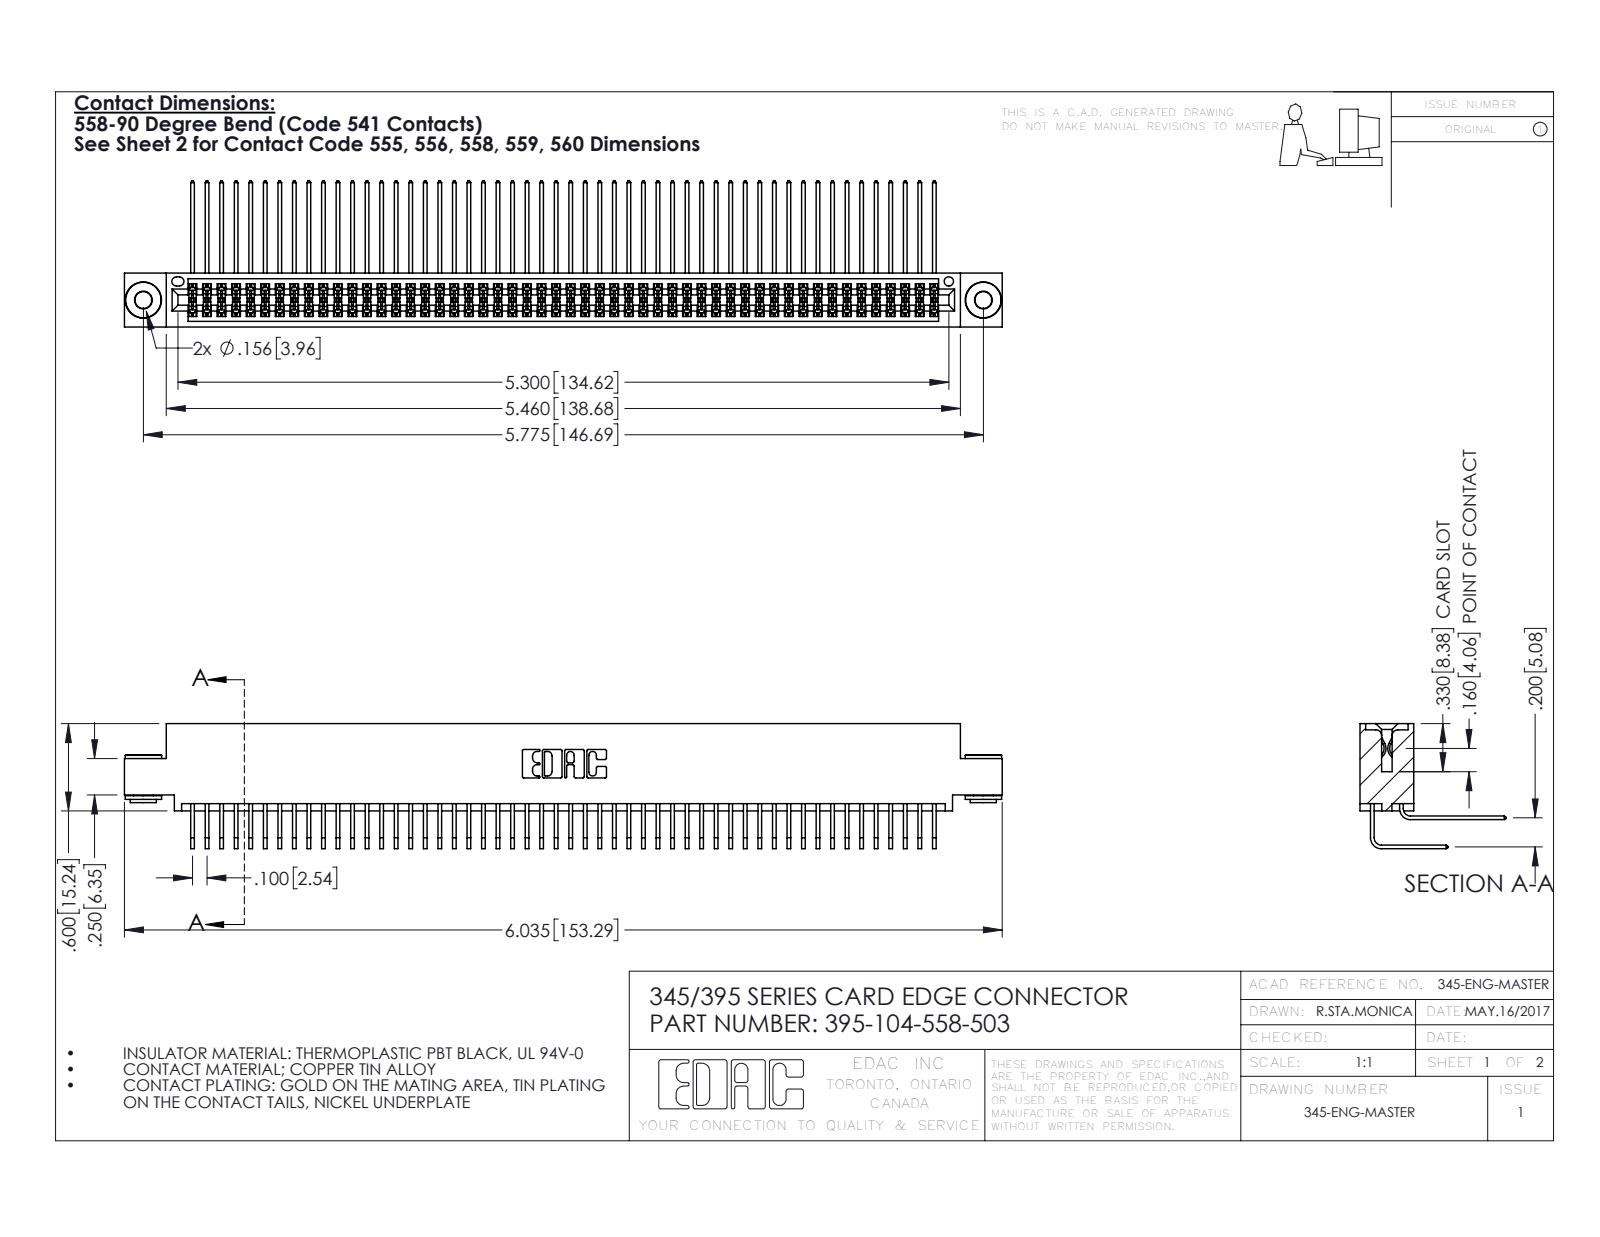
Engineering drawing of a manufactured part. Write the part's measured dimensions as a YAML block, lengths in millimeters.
part_name: "395-104-558-503; 345-292-001_558 559 Tail - 1; 345-250-002_345-250-002-102; 345-292-001_558 Tail - 2 (+1 more)"
step_written_by: "SolidWorks 2016 (CONFIG_CONTROL_DESIGN)"
units: millimeters
bodies: {solids: 107, faces: 5576, planar: 3734, cylindrical: 1834, other: 8}
overall_size: [153.3, 25.5, 21.8]
volume: 15500
surface_area: 26270
round_holes:
  - {diameter: 2.9, count: 2}
  - {diameter: 4, count: 2}
  - {diameter: 1.6, count: 1}
round_bosses_or_shafts:
  - {diameter: 6.4, count: 2}
  - {diameter: 4.6, count: 2}
  - {diameter: 3.5, count: 2}
partial_cylinders:
  - {radius: 0.2, count: 157}
  - {radius: 0.3, count: 22}
  - {radius: 0.2, count: 6}
  - {radius: 0.8, count: 6}
  - {radius: 0.7, count: 3}
  - {radius: 0.4, count: 2}
  - {radius: 0.5, count: 2}
  - {radius: 0.6, count: 2}
face_to_face_distances: [1.8, 7.6, 5.1, 0.6, 9.4, 2.5, 6.9, 5.7, 0.6, 4.4]
hole_center_spacings: [6.9, 140.7, 146.7]
